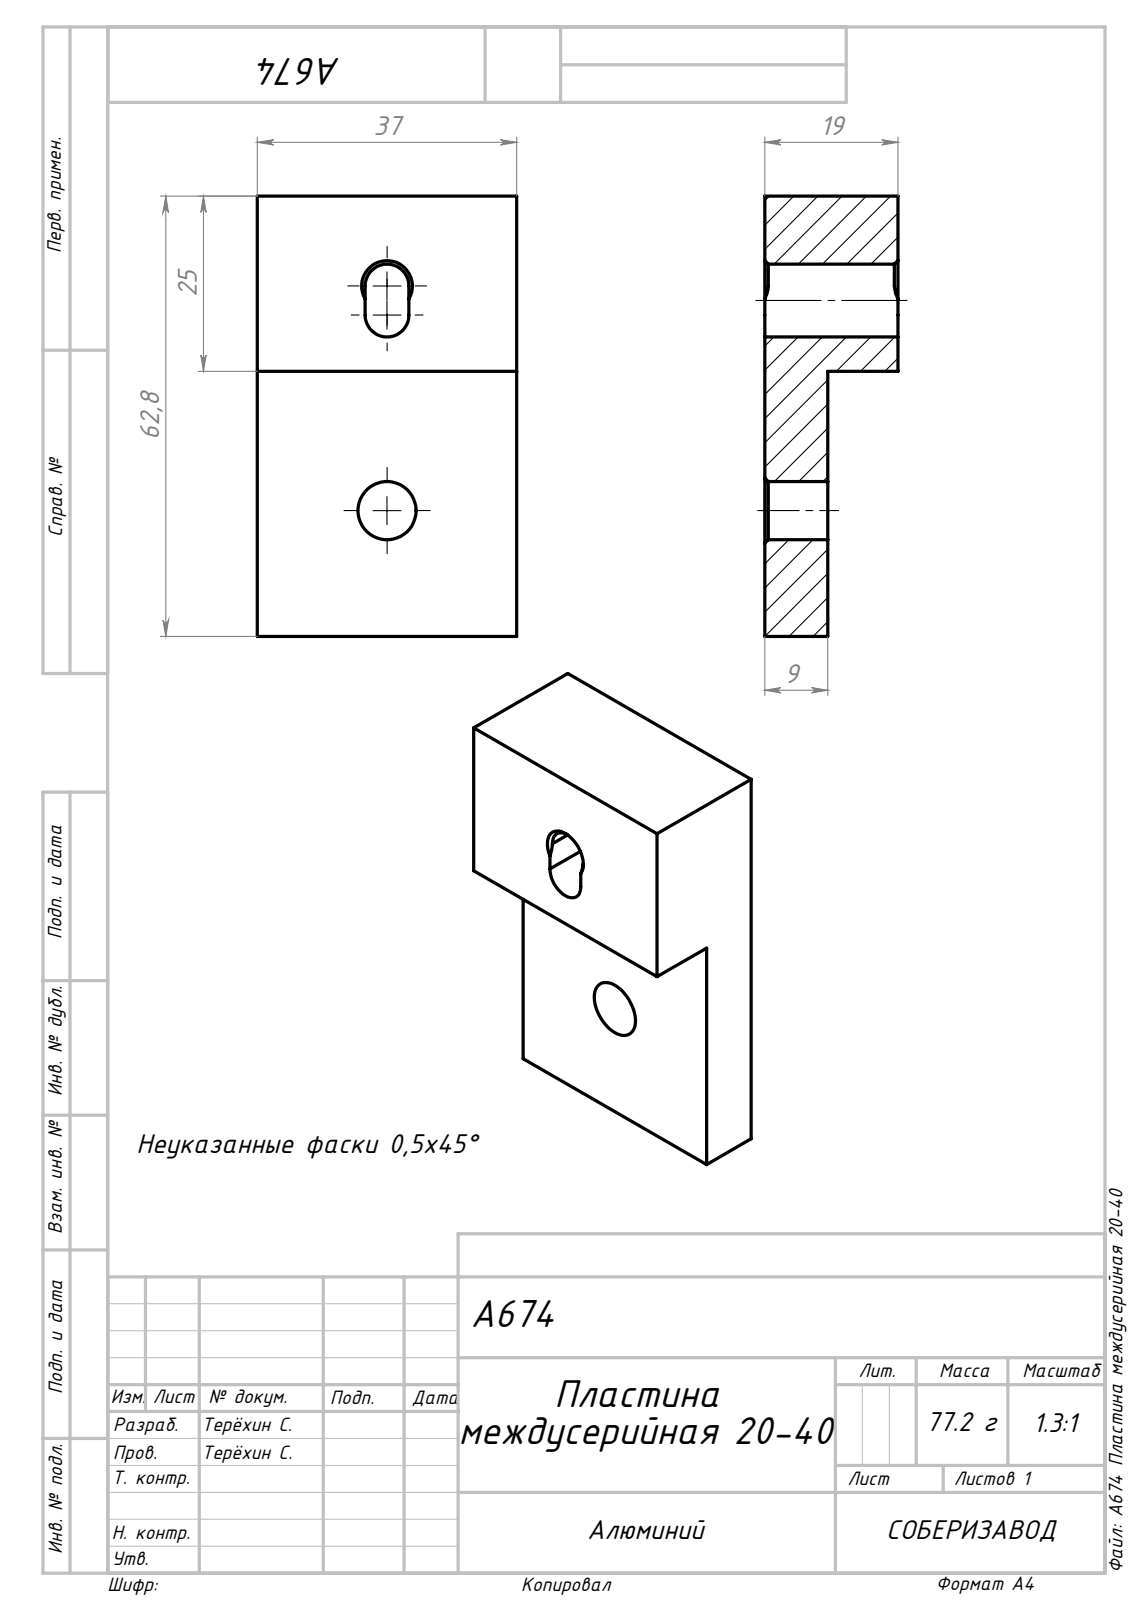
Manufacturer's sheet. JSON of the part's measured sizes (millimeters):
{"part_name": "A674 Пластина междусерийная 20-40", "step_written_by": "SolidWorks 2022 (AUTOMOTIVE_DESIGN)", "units": "millimeters", "bodies": {"solids": 1, "faces": 22, "planar": 10, "cylindrical": 4, "other": 8}, "overall_size": [62.85, 37, 19], "volume_mm3": 28610, "surface_area_mm2": 8218, "round_holes": [[8.3, 1]], "partial_cylinders_radius": [[3.12, 2]], "face_to_face_distances": [9, 19, 10, 37, 25, 37.85, 62.85, 15.38, 21.62, 6.24]}
